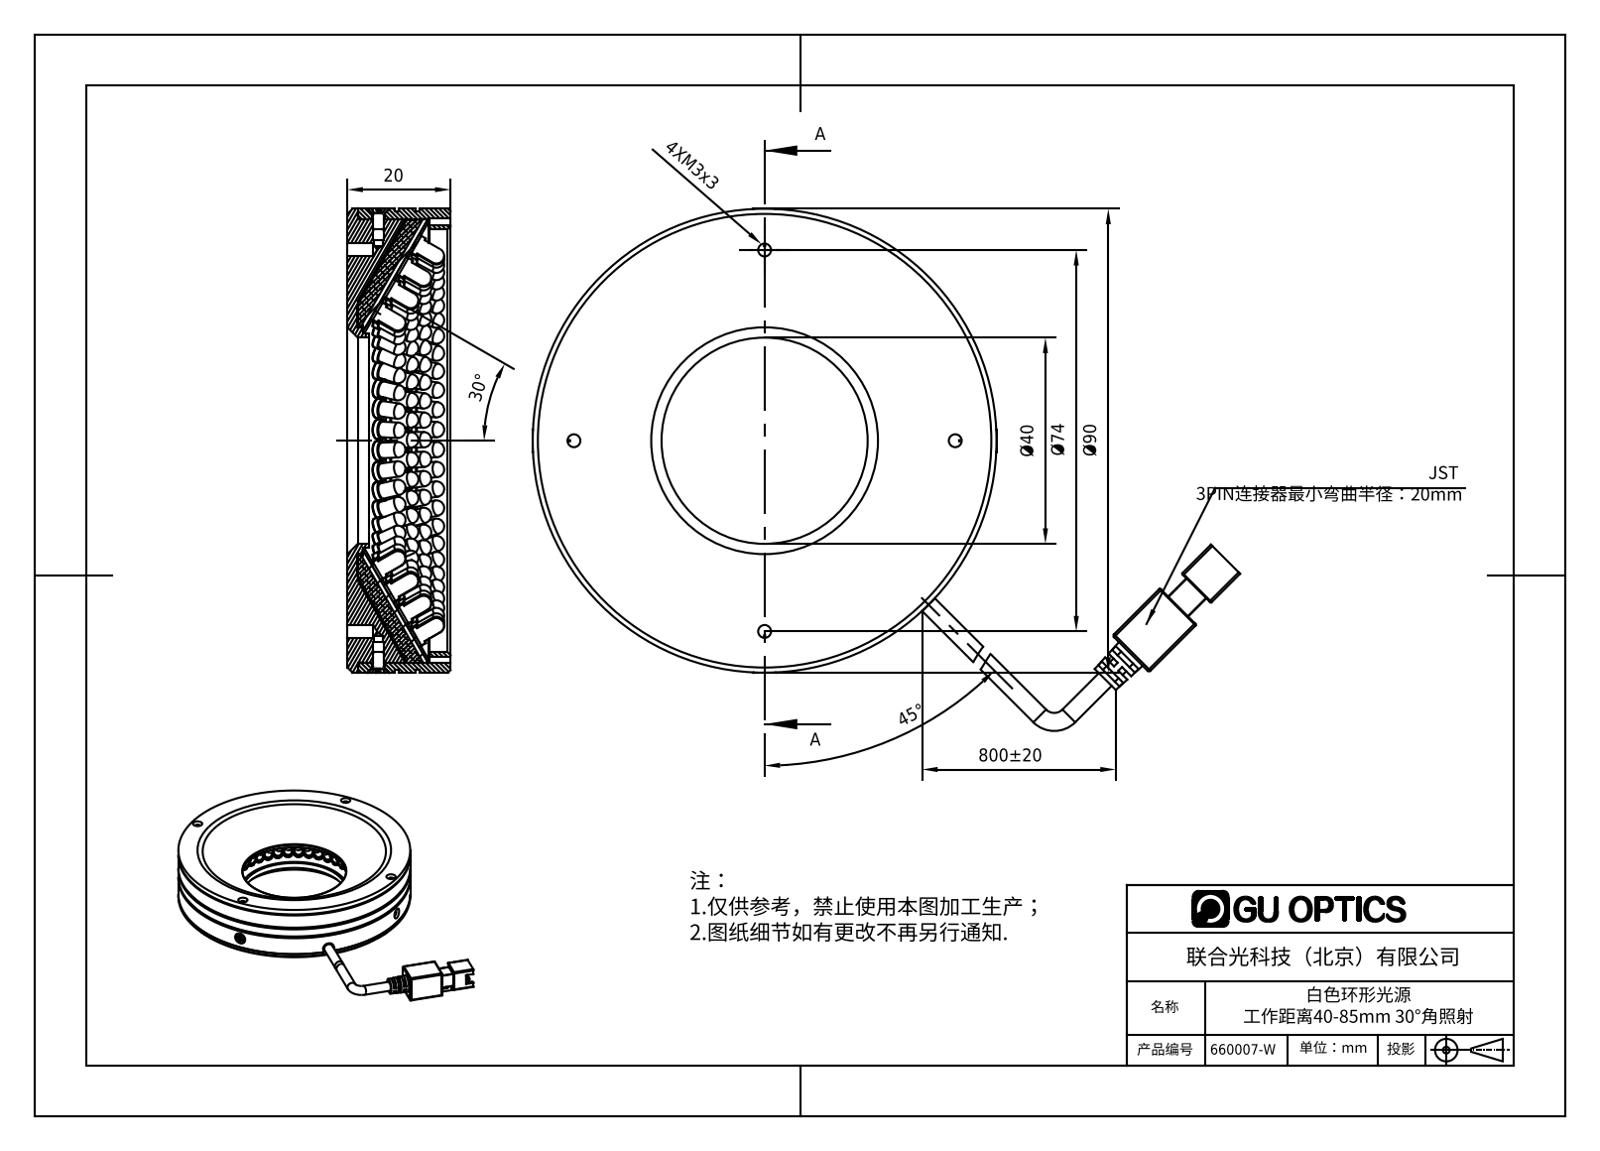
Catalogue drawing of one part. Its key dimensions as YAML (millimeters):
part_name: "660007-W"
step_written_by: "SolidWorks 2016 (AUTOMOTIVE_DESIGN)"
units: millimeters
bodies: {solids: 201, faces: 4314, planar: 2669, cylindrical: 1337, other: 308}
overall_size: [137.28, 101.31, 24.15]
volume: 78786
surface_area: 78720
round_holes:
  - {diameter: 1.25, count: 4}
  - {diameter: 1.8, count: 4}
  - {diameter: 2.5, count: 4}
  - {diameter: 1.6, count: 2}
  - {diameter: 2, count: 2}
  - {diameter: 2.4, count: 2}
  - {diameter: 40, count: 1}
  - {diameter: 44, count: 1}
  - {diameter: 82, count: 1}
round_bosses_or_shafts:
  - {diameter: 3.8, count: 248}
  - {diameter: 3, count: 192}
  - {diameter: 3.5, count: 2}
  - {diameter: 90, count: 1}
  - {diameter: 89, count: 1}
  - {diameter: 86, count: 1}
  - {diameter: 44.6, count: 1}
  - {diameter: 41.7, count: 1}
partial_cylinders:
  - {radius: 0.2, count: 37}
  - {radius: 0.1, count: 15}
  - {radius: 0.4, count: 12}
  - {radius: 0.3, count: 1}
  - {radius: 0.68, count: 1}
  - {radius: 1.4, count: 1}
  - {radius: 1.65, count: 1}
  - {radius: 9, count: 1}
face_to_face_distances: [20, 2, 22, 18, 1, 0.5, 4, 6, 3, 14]
hole_center_spacings: [5.5, 42.5, 56.35, 79.5, 85, 60.1, 37, 52.33]
